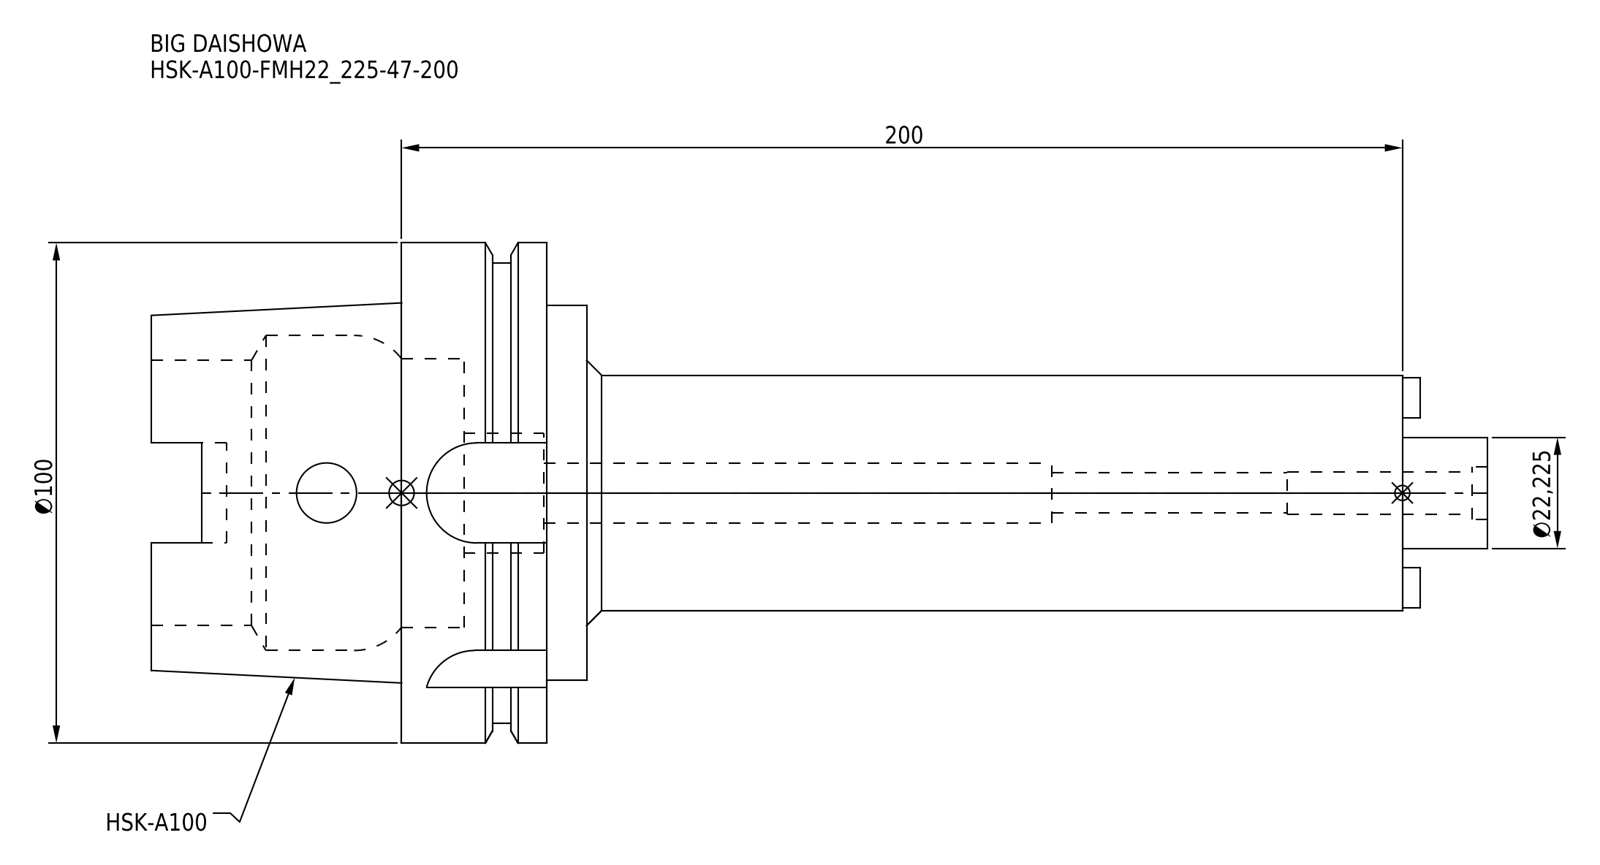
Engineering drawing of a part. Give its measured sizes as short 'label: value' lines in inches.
name: HSK-A100-FMH22_225-47-200
written by: CREO PARAMETRIC BY PTC INC, 2016380 (AUTOMOTIVE_DESIGN)
unit: in
bodies: 1 solid, 109 faces (47 planar, 46 cylindrical, 16 other)
size: 10.512 × 3.937 × 3.937
volume: 34.37 in³; area: 128.8 in²
holes: 2× ⌀0.472, 1× ⌀0.315, 1× ⌀0.335, 1× ⌀0.413, 1× ⌀0.945, 1× ⌀2.087, 1× ⌀2.118, 1× ⌀2.48
bosses: 1× ⌀3.937, 1× ⌀3.622, 1× ⌀2.953, 1× ⌀1.85, 1× ⌀0.875
rounds: 4× R0.192, 4× R0.394
face distances: 1.142, 0.315, 1.457, 0.967, 0.652, 0.49, 6.417, 6.732, 7.384, 7.874
